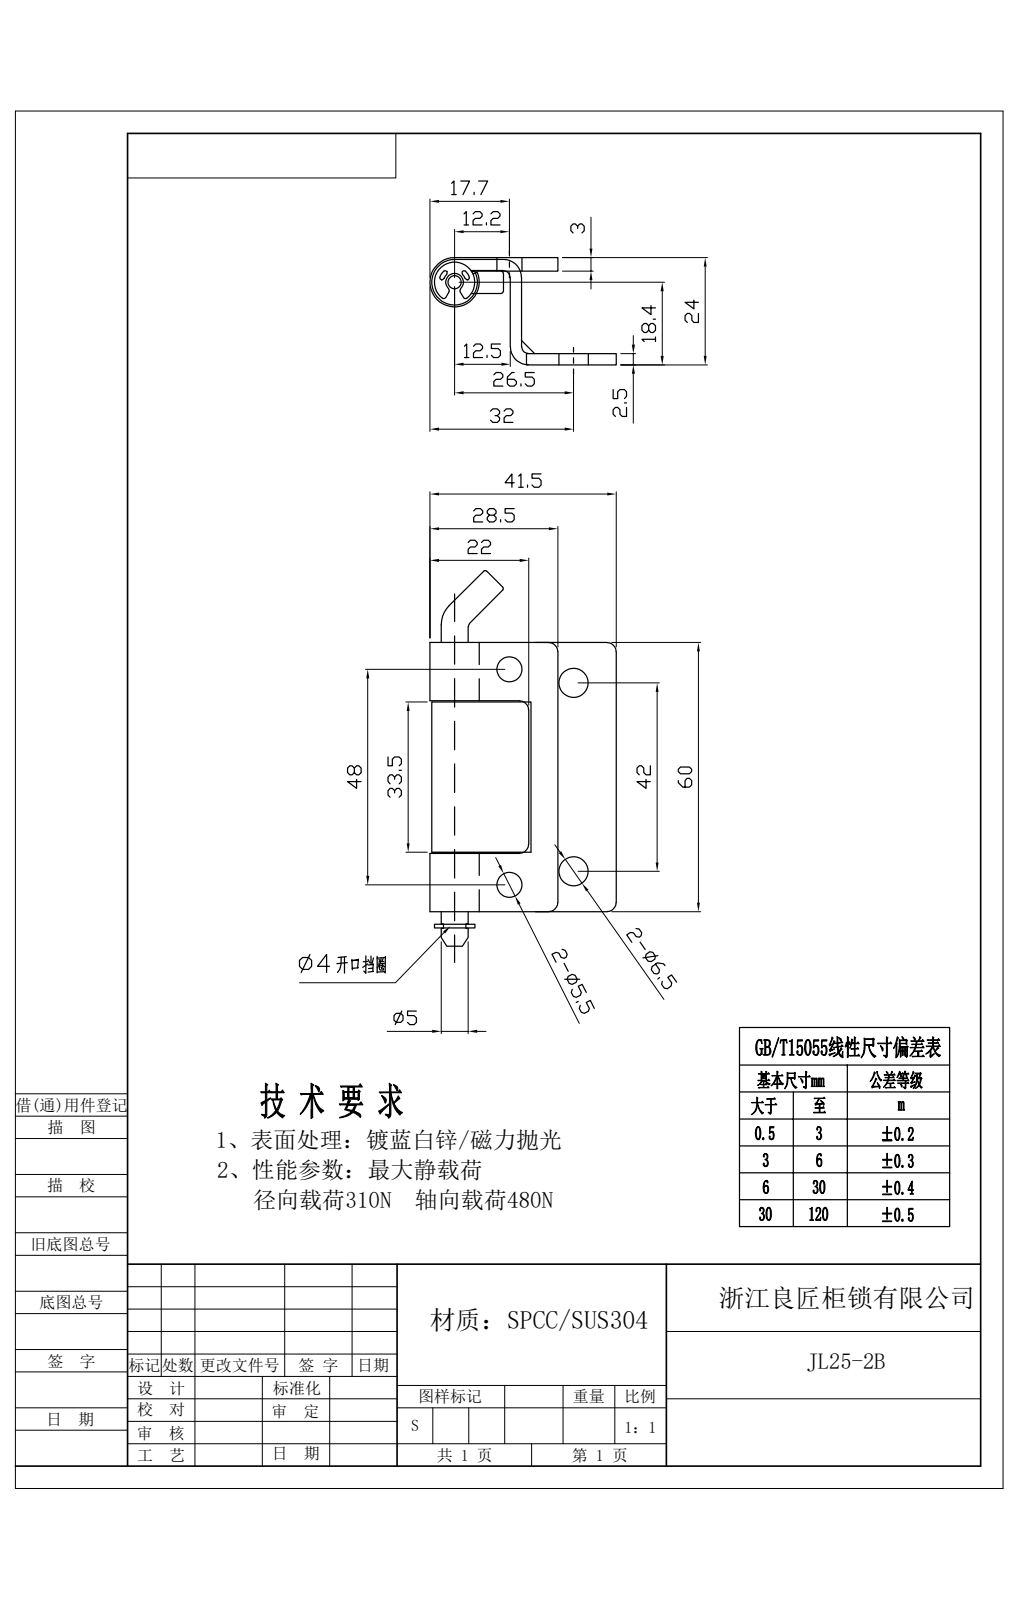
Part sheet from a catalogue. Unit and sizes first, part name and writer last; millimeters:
Units: millimetres
Overall size (bounding box): 84.46 × 41.5 × 23.9
Round holes (diameter × count): ⌀5.5 ×2, ⌀6.5 ×2, ⌀4 ×1, ⌀5 ×1, ⌀5.2 ×1
Round bosses / shafts (diameter × count): ⌀11 ×1, ⌀10.2 ×1, ⌀6 ×1, ⌀5 ×1
Partial cylindrical surfaces — rounded edges, fillets, slot ends (radius × count): R2 ×10, R0.5 ×4, R1.5 ×4, R4 ×2, R3.5 ×1, R4.5 ×1
Main face-to-face distances: 2.5, 3, 20.9, 18.4, 23.9, 21.4, 21, 23.5, 18.5, 2.6
Hole centre spacings: 14.61, 47.22, 42, 48
Volume: 13 007 mm³ · Surface area: 11 769 mm²
Bodies: 4 solids, 101 faces (43 planar, 54 cylindrical, 4 other)
STEP written by: Rhino 8.5 (CONFIG_CONTROL_DESIGN)
